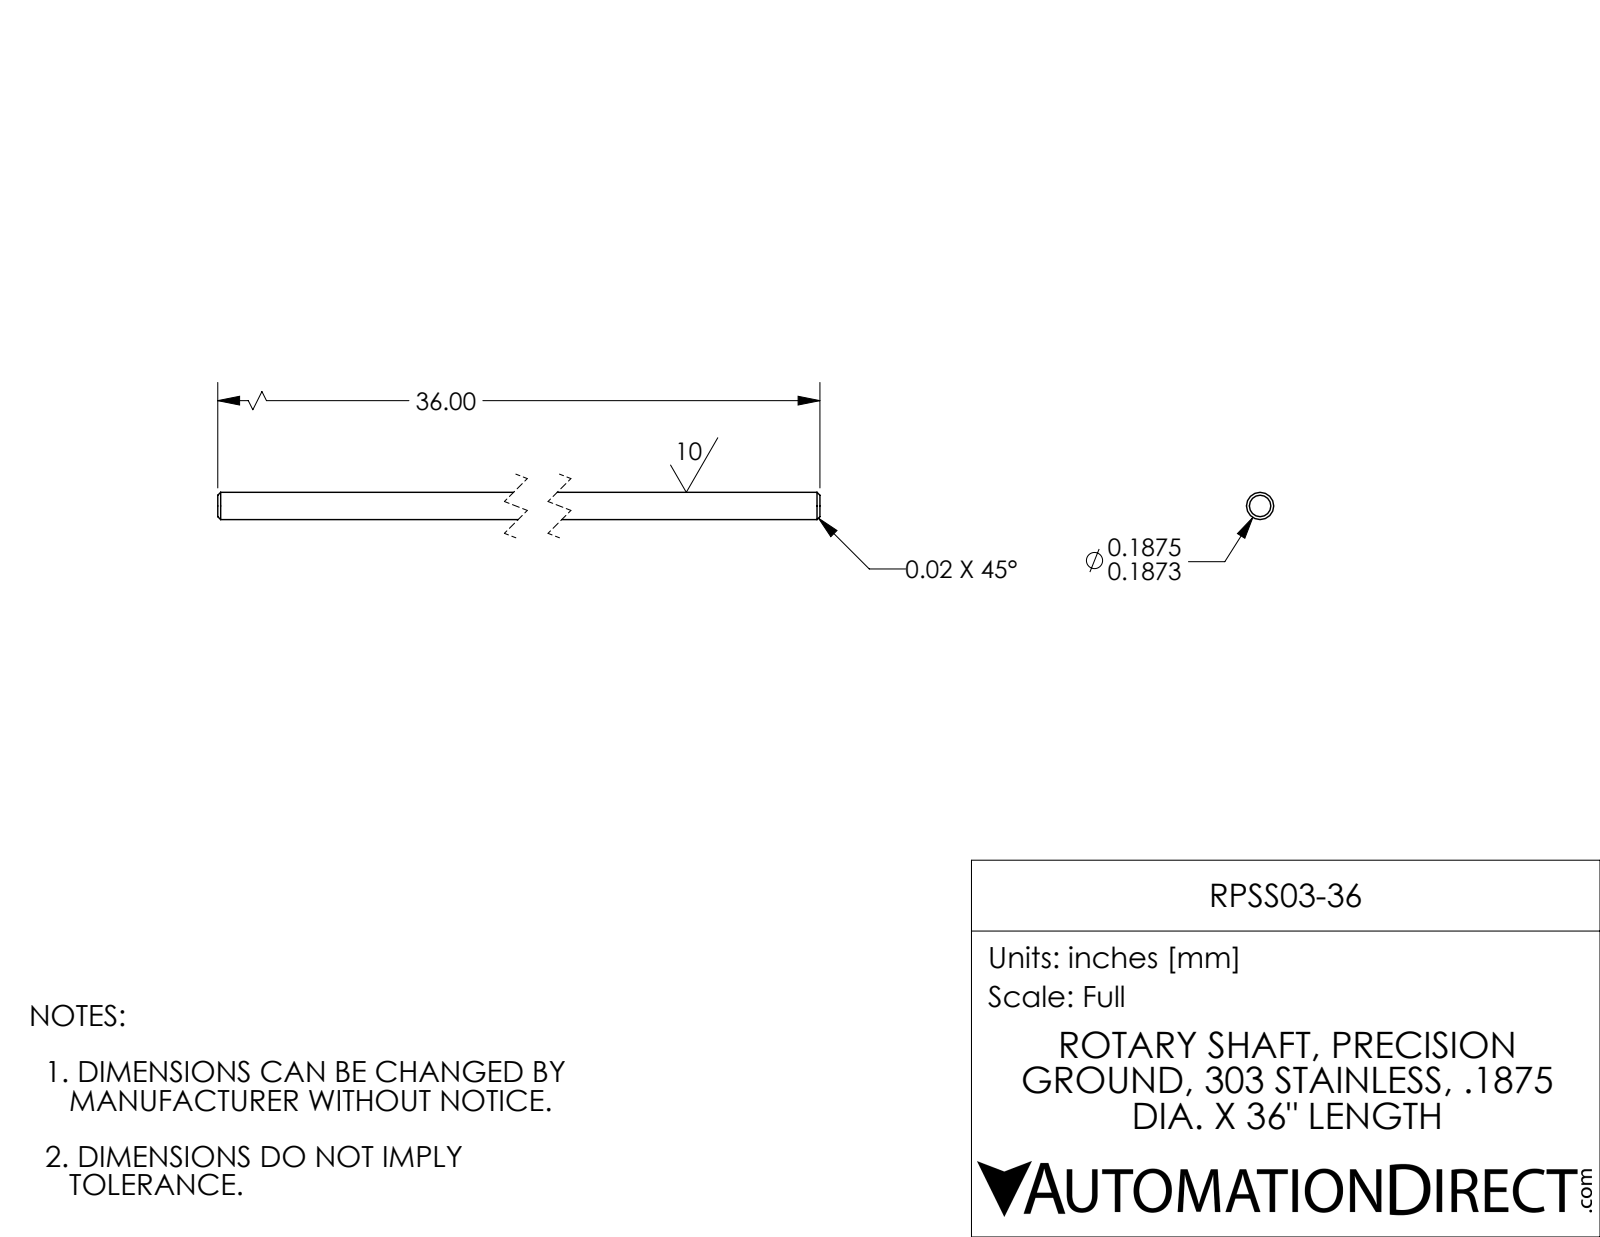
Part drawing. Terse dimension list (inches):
name: RPSS03-36
written by: SolidWorks 2017 (AUTOMOTIVE_DESIGN)
unit: in
bodies: 1 solid, 8 faces (2 planar, 2 cylindrical, 4 other)
size: 36 × 0.188 × 0.188
volume: 0.994 in³; area: 21.25 in²
bosses: 1× ⌀0.187
face distances: 36
